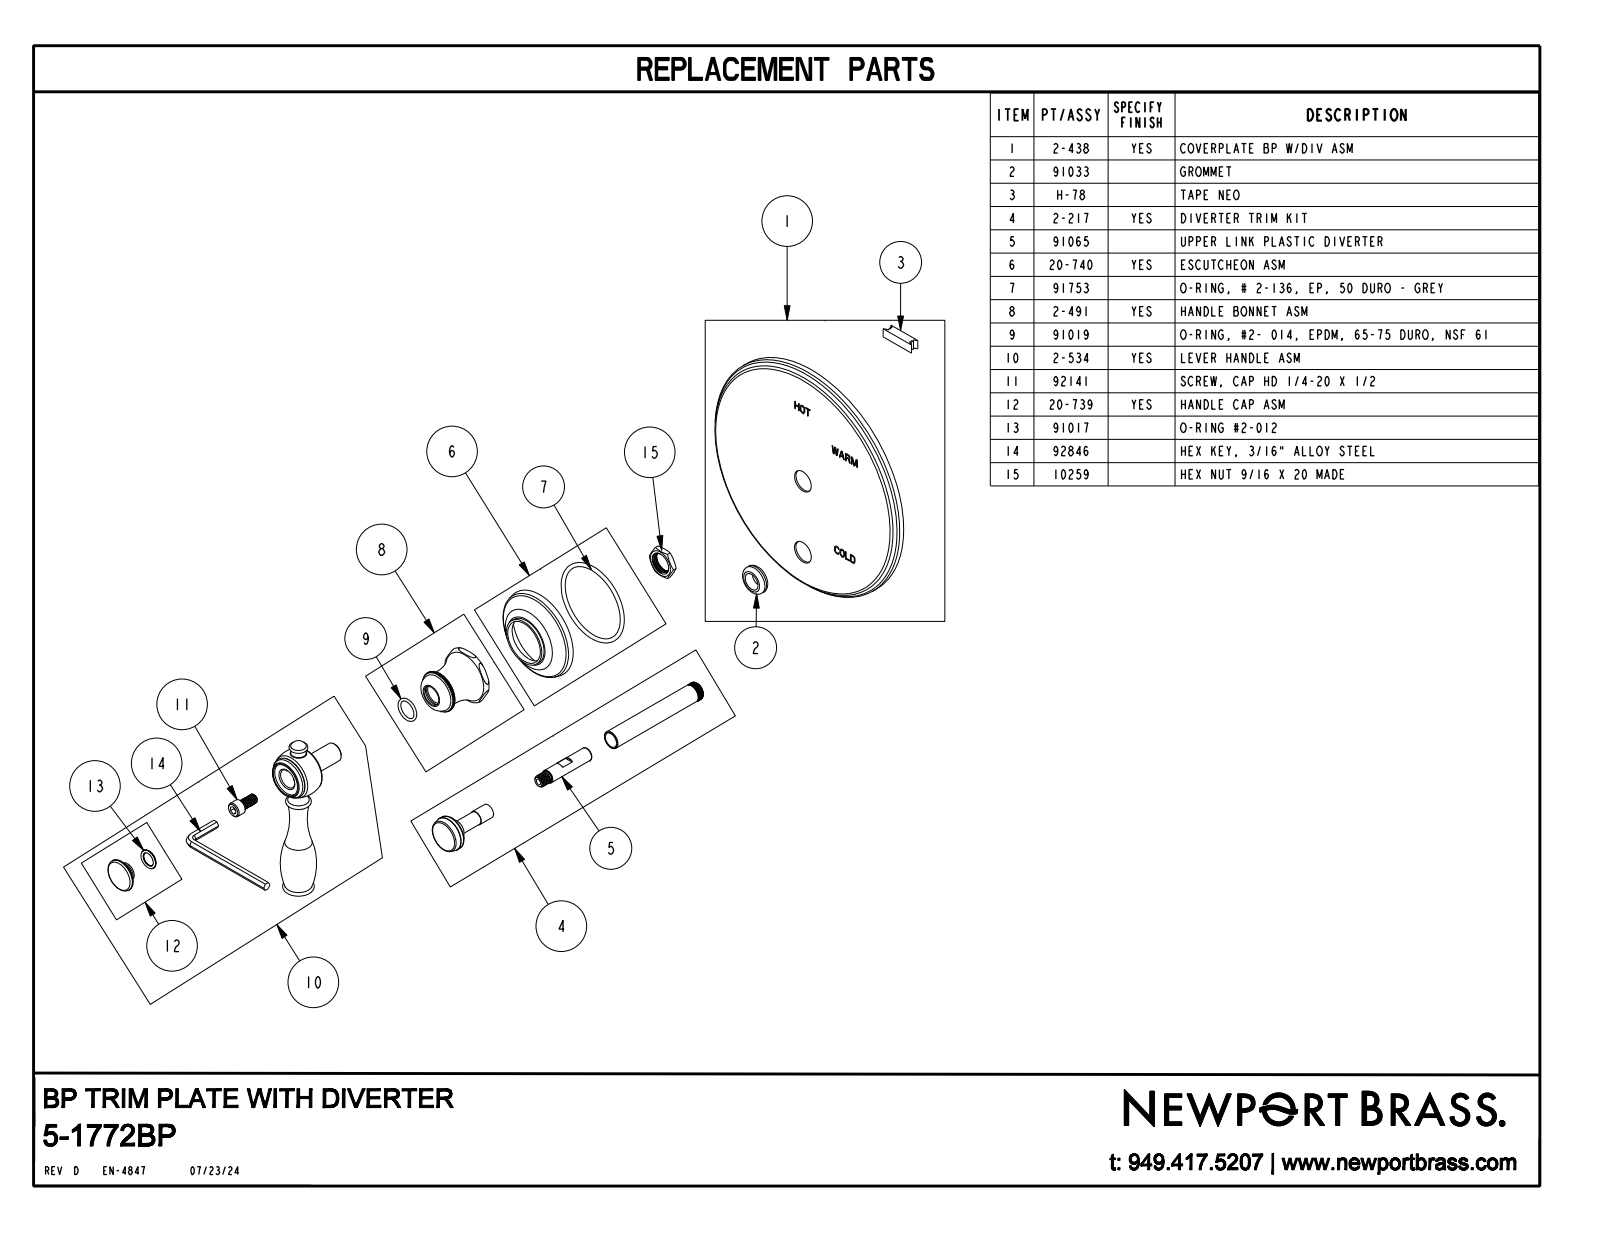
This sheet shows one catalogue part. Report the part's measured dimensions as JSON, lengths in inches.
{"part_name": "5-1772BP", "step_written_by": "CREO PARAMETRIC BY PTC INC, 2018400 (CONFIG_CONTROL_DESIGN)", "units": "inches", "bodies": {"solids": 1, "faces": 517, "planar": 419, "cylindrical": 22, "other": 76}, "overall_size": [6.896, 6.5, 3.723], "volume_in3": 15.32, "surface_area_in2": 92.83, "round_holes": [[0.41, 1], [0.855, 1]], "round_bosses_or_shafts": [[6.5, 1], [0.9, 1], [0.84, 1], [0.5, 1], [0.472, 1], [0.392, 1], [0.354, 1]], "face_to_face_distances": [0.313, 1.665, 1.352, 2.853, 2.54, 1.188, 1.375, 0.309, 1.356, 2.544]}
